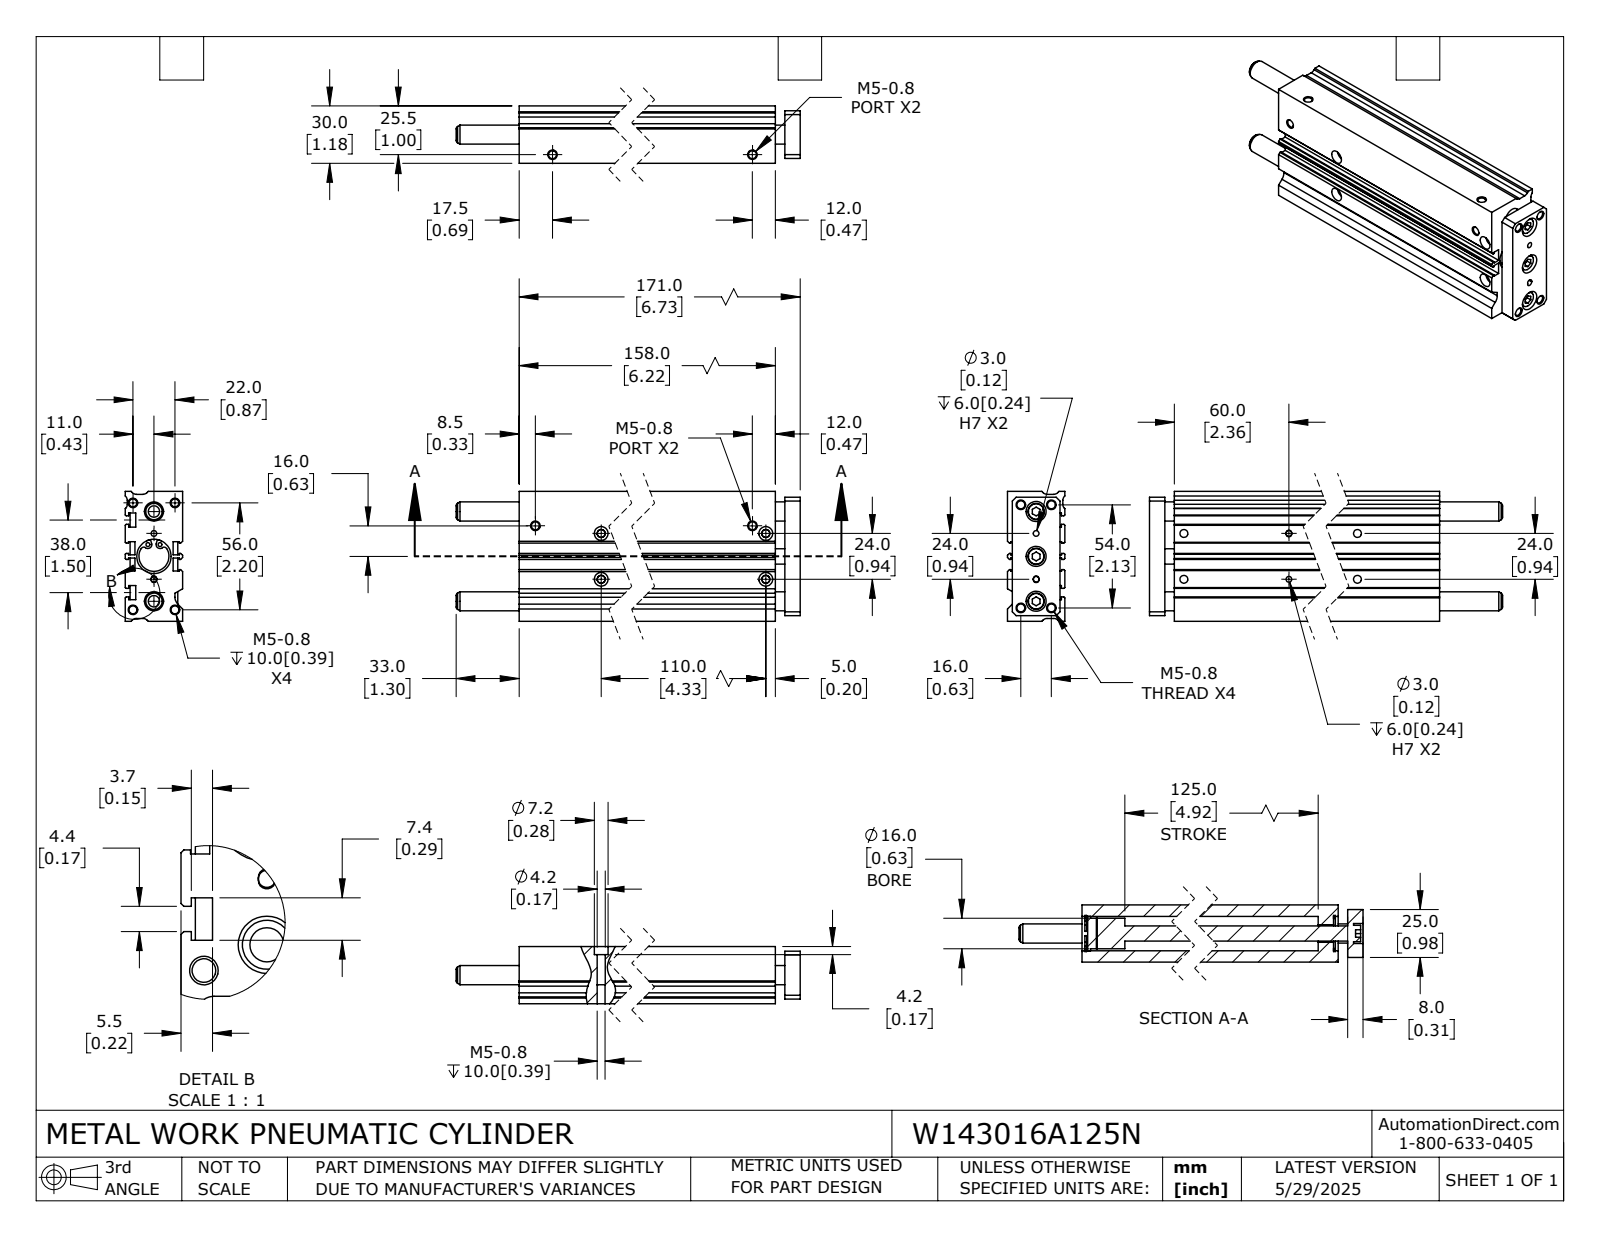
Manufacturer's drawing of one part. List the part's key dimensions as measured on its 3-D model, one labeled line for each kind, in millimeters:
Part name (STEP PRODUCT): W143016A125N; W143016A125N_ROD; W143016A125N_BODY
STEP written by: SolidWorks 2024 (CONFIG_CONTROL_DESIGN)
Units: millimetres
Bodies: 5 solids, 344 faces (169 planar, 137 cylindrical, 38 other)
Overall size (bounding box): 204 × 68 × 30
Volume: 268 325 mm³ · Surface area: 93 202 mm²
Round holes (diameter × count): ⌀4.13 ×16, ⌀2 ×4, ⌀3 ×4, ⌀4.2 ×4, ⌀7.2 ×4, ⌀10.5 ×3, ⌀10 ×2, ⌀9.2 ×1, ⌀15.7 ×1, ⌀18 ×1
Round bosses / shafts (diameter × count): ⌀8.5 ×3, ⌀19 ×2, ⌀16 ×1, ⌀8 ×1
Partial cylindrical surfaces — rounded edges, fillets, slot ends (radius × count): R3 ×6, R1.5 ×4, R1.58 ×4, R2.07 ×4, R5 ×1
Main face-to-face distances: 5, 30, 25, 68, 1.5, 5.5, 0.5, 33.15, 24.5, 2.5
Hole centre spacings: 3.16, 6.62, 6.95, 8.73, 11.88, 17, 17.6, 18.46
